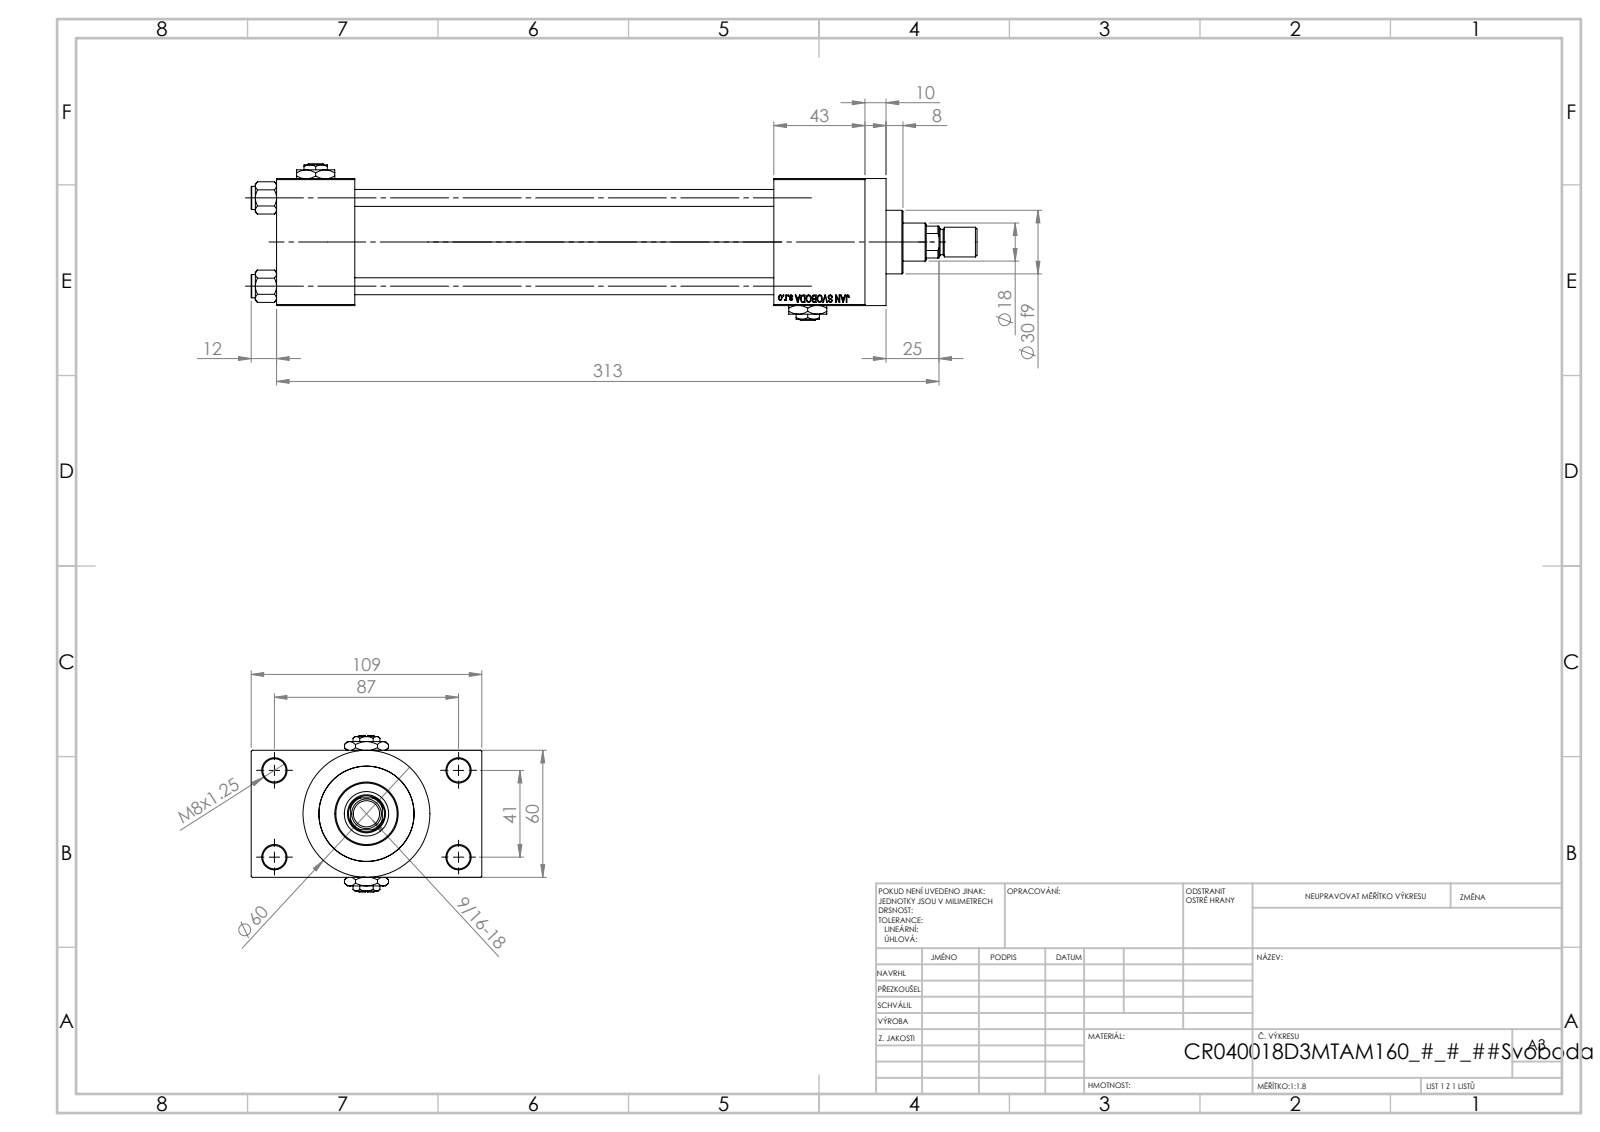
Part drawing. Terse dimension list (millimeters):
name: Zatka_pro_OIL_PORT; V215CR_VCP_D; V215CR_D_Body; NUT_M5_D (+3 more)
written by: SolidWorks 2019 (CONFIG_CONTROL_DESIGN)
unit: mm
bodies: 14 solids, 1203 faces (546 planar, 93 cylindrical, 564 other)
size: 343 × 109 × 74
volume: 643 838 mm³; area: 184 020 mm²
holes: 4× ⌀8, 4× ⌀11, 2× ⌀7, 2× ⌀16.66, 2× ⌀24, 1× ⌀8.5, 1× ⌀18, 1× ⌀21, 1× ⌀31, 1× ⌀40, 1× ⌀45
bosses: 4× ⌀11, 1× ⌀60, 1× ⌀46, 1× ⌀30, 1× ⌀14, 1× ⌀12
rounds: 1× R8.5
face distances: 60, 24.5, 84.5, 198, 37, 235, 43, 278, 241, 109
hole spacings: 22.65, 29.49, 41.7, 47.15, 48.09, 64.35, 76.49, 41
